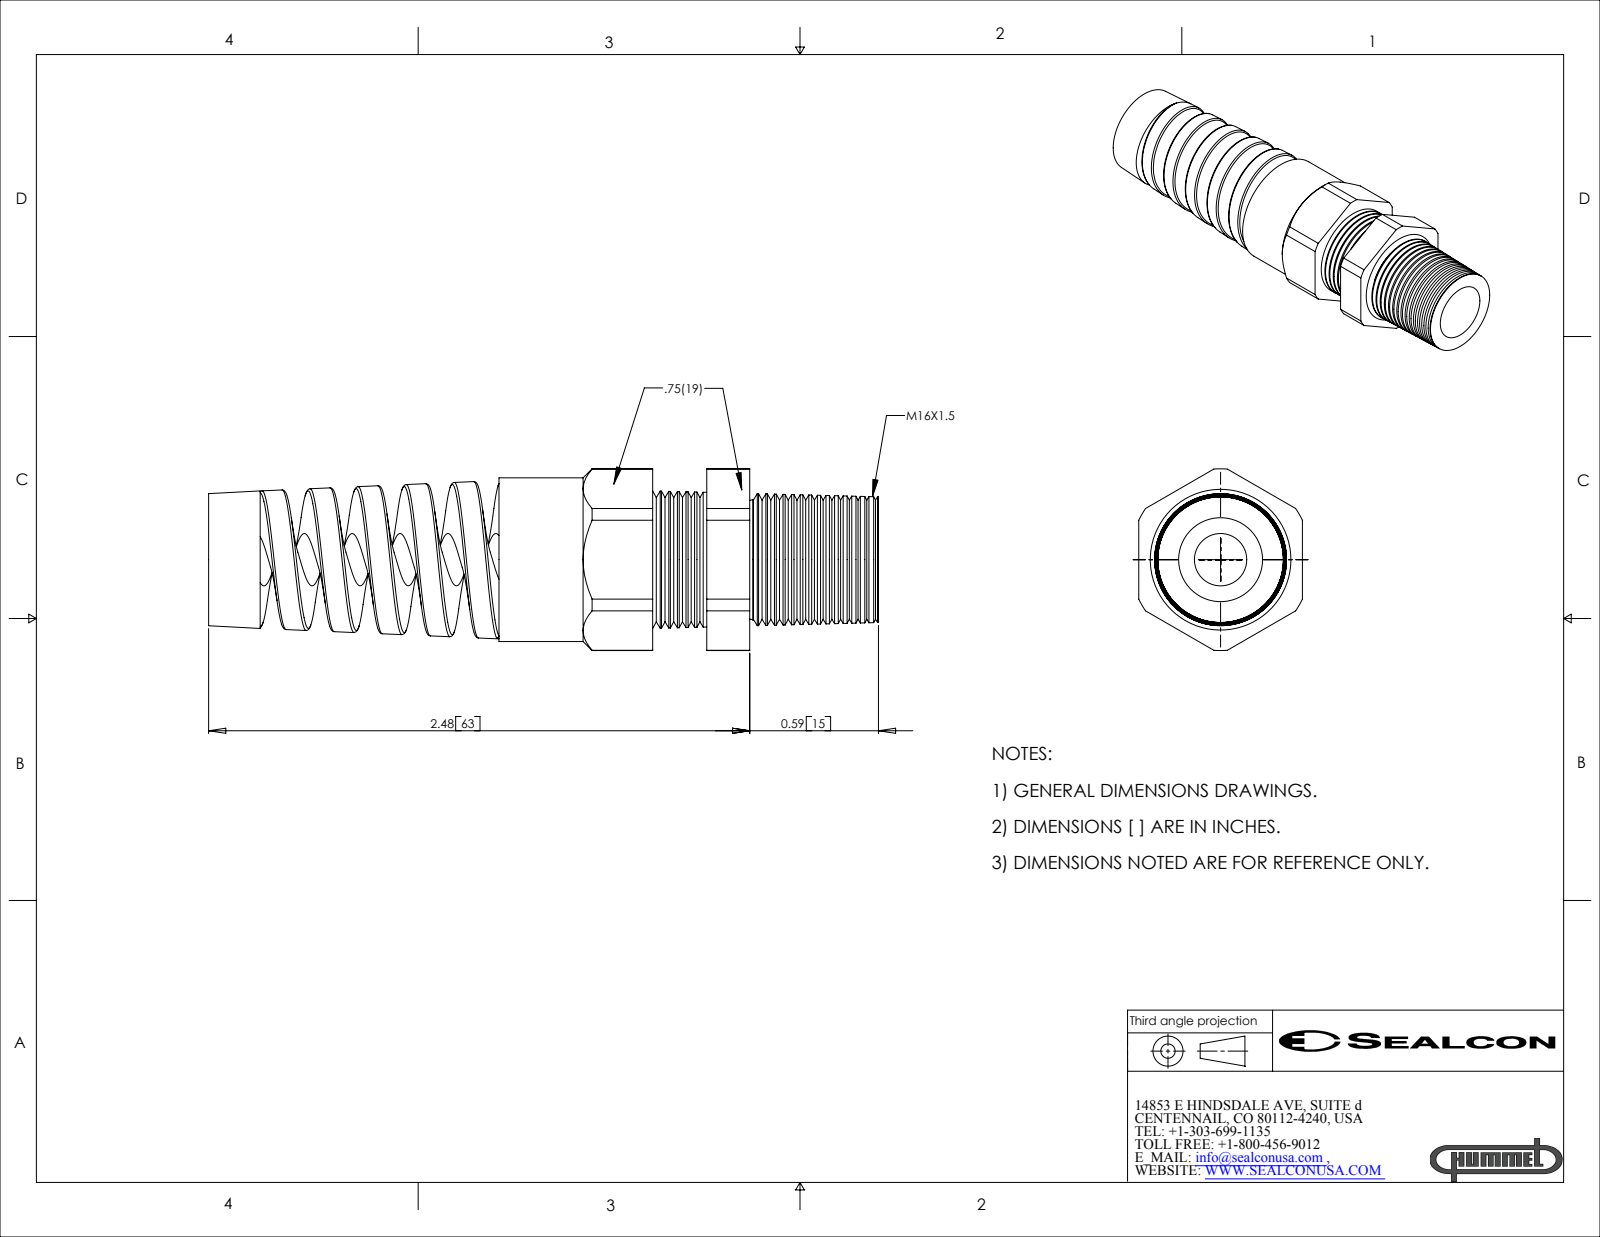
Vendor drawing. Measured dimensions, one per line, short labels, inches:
name: CF16DR-BK
written by: SolidWorks 2007 (CONFIG_CONTROL_DESIGN)
unit: in
bodies: 2 solids, 220 faces (25 planar, 35 cylindrical, 160 other)
size: 3.07 × 0.833 × 0.75
volume: 0.798 in³; area: 13.78 in²
holes: 1× ⌀0.24, 1× ⌀0.265
bosses: 1× ⌀0.75, 1× ⌀0.547
rounds: 1× R0.416
face distances: 0.75, 1.717, 2.283, 0.567, 1.331, 0.385, 0.952, 0.75, 1.63, 0.299
